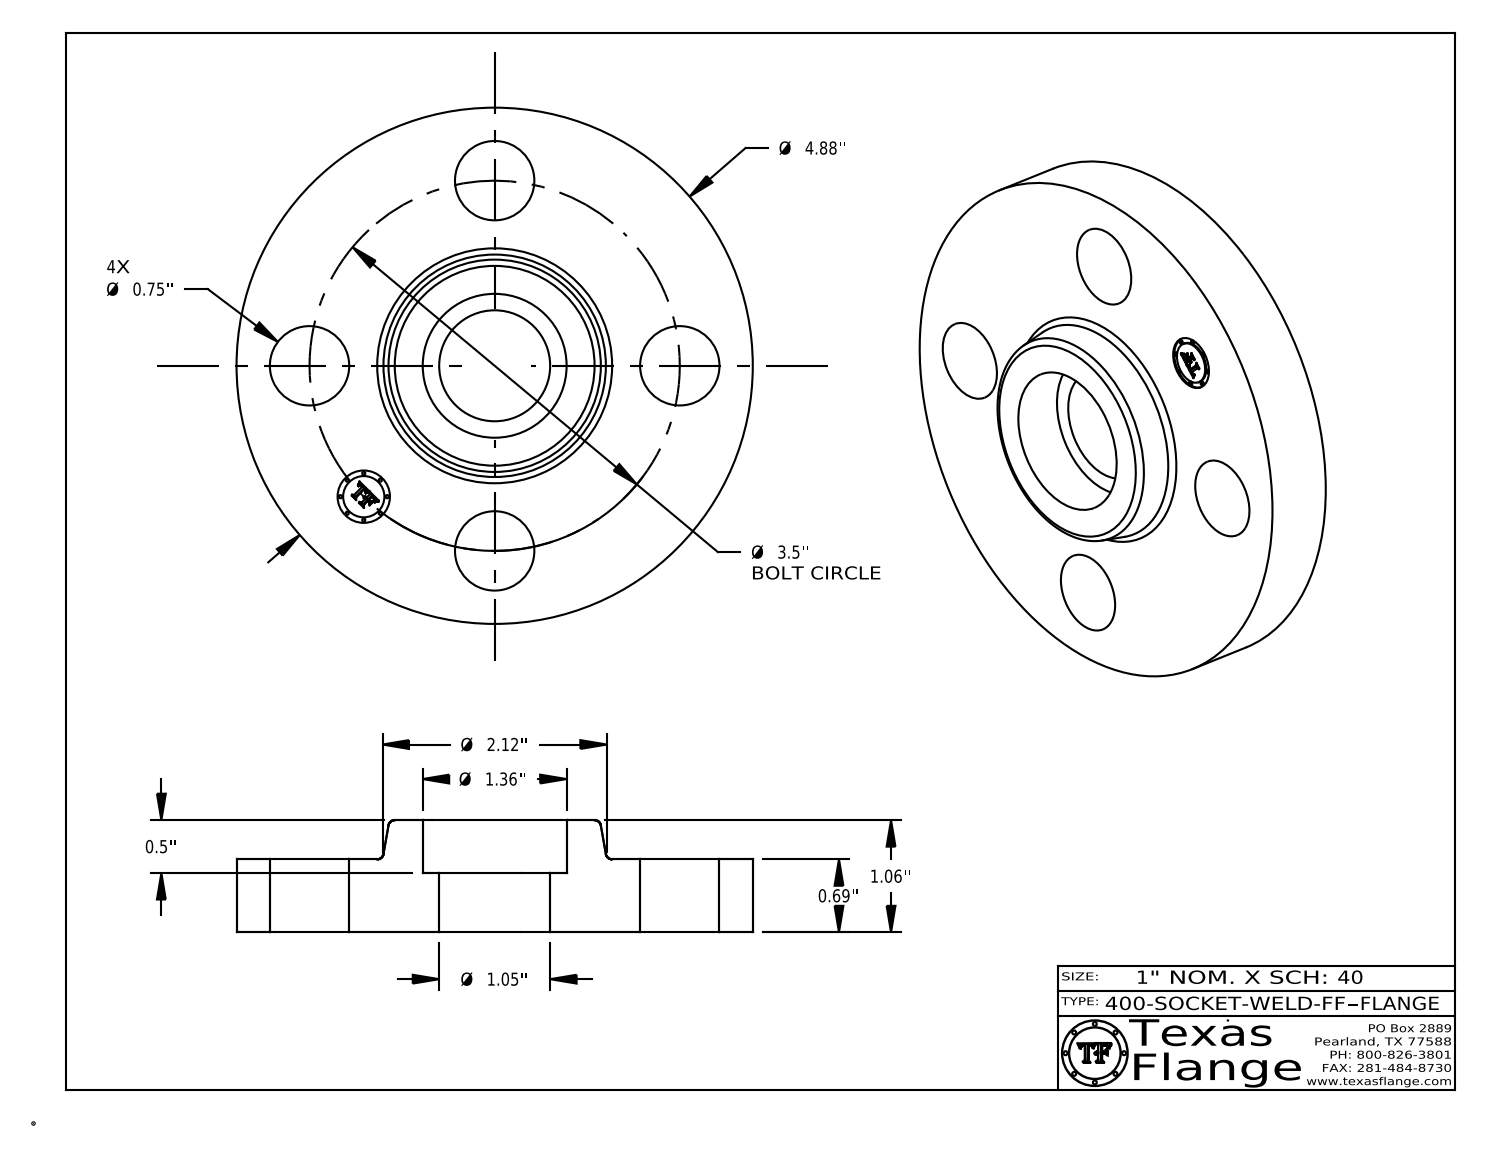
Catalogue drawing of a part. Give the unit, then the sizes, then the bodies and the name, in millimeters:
Units: millimetres
Overall size (bounding box): 124 × 124 × 26.9
Round holes (diameter × count): ⌀19.1 ×4, ⌀12.6 ×1, ⌀26.6 ×1, ⌀34.5 ×1
Round bosses / shafts (diameter × count): ⌀0.8 ×8, ⌀124 ×1, ⌀9.9 ×1
Main face-to-face distances: 17.5, 26.9, 9.4, 14.2, 3.3, 12.7, 0.4, 17.1, 2.9, 9.8
Hole centre spacings: 44.5, 62.9, 34, 82.1, 88.9
Volume: 191 700 mm³ · Surface area: 35 540 mm²
Bodies: 1 solid, 409 faces (369 planar, 34 cylindrical, 6 other)
Part name (STEP PRODUCT): 400-SOCKET-WELD-FF
STEP written by: CATIA V5 STEP AP214 (AUTOMOTIVE_DESIGN)
